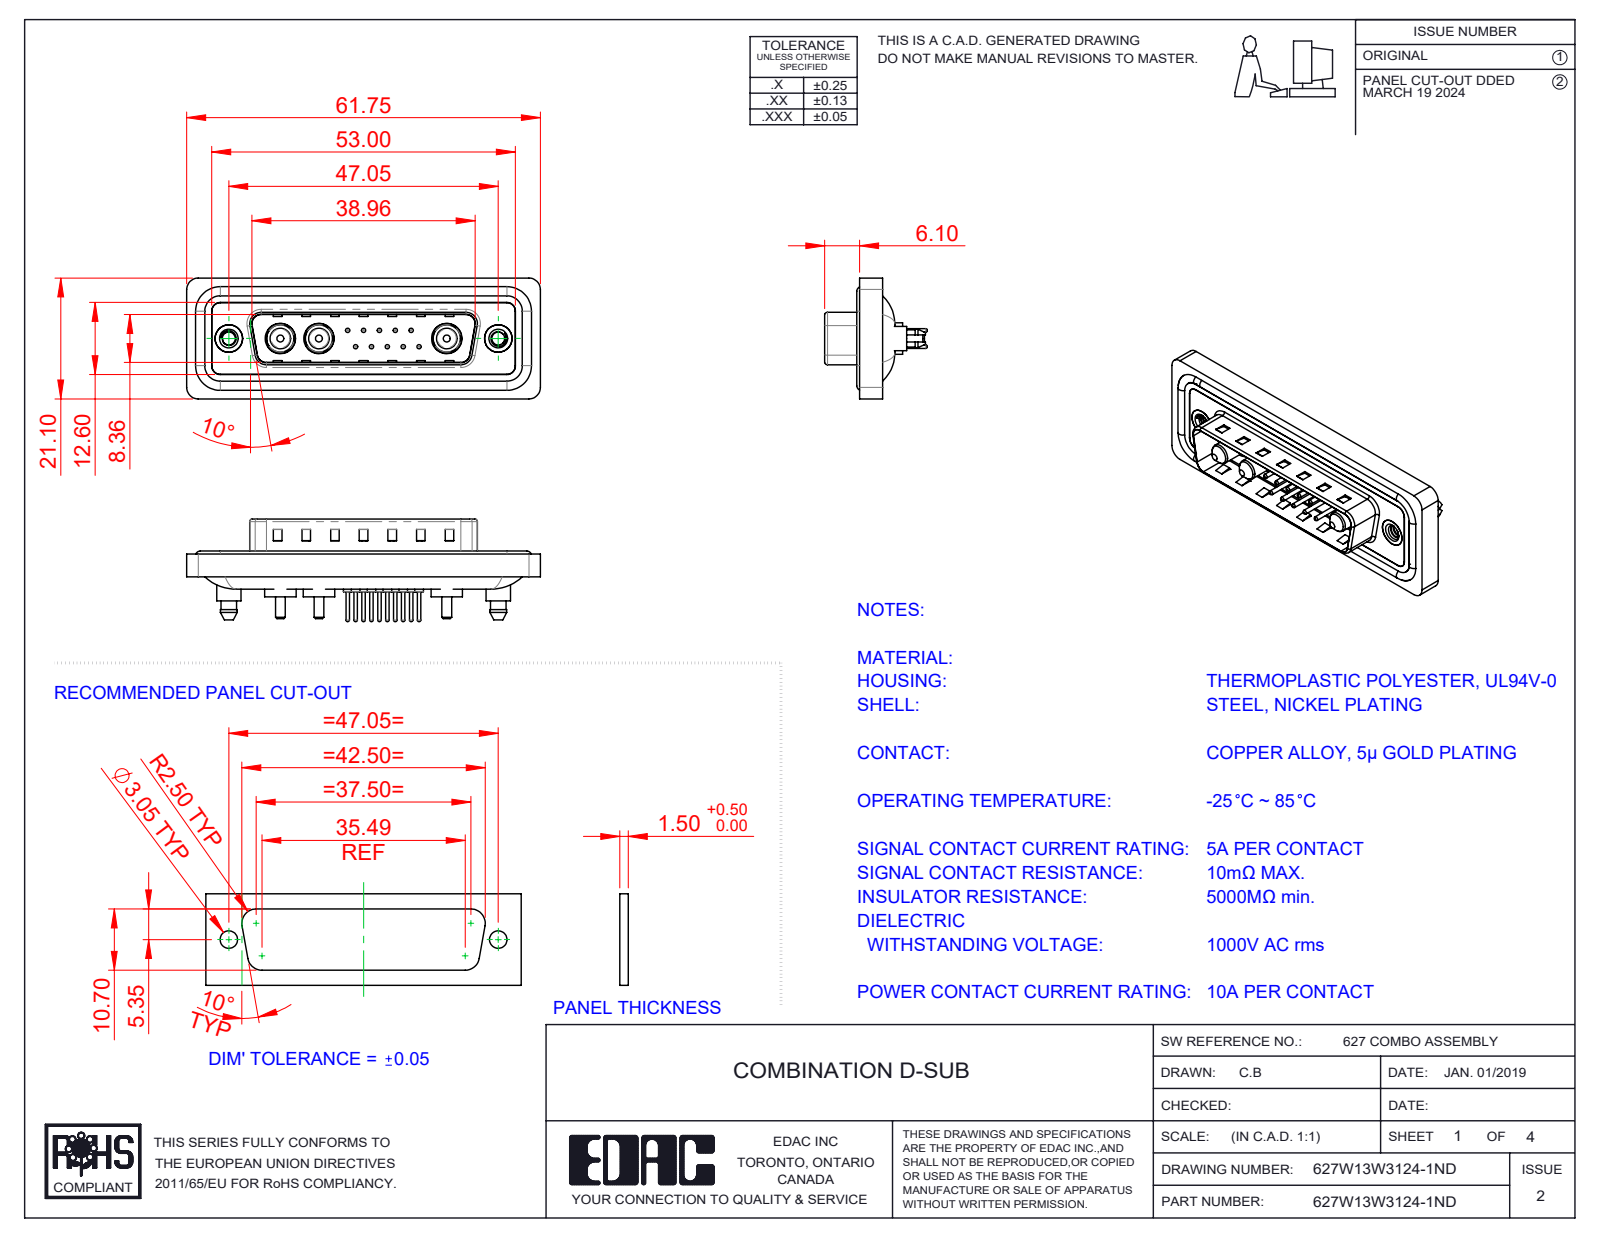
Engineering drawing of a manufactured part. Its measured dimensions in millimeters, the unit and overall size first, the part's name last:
Units: millimetres
Overall size (bounding box): 61.75 × 21.1 × 17.9
Round holes (diameter × count): ⌀0.75 ×10, ⌀1.6 ×10, ⌀2 ×10, ⌀4.85 ×3, ⌀5.3 ×3, ⌀2.26 ×2, ⌀4 ×2, ⌀4.8 ×2, ⌀5 ×2
Round bosses / shafts (diameter × count): ⌀1.5 ×10, ⌀0.6 ×10, ⌀1.6 ×4, ⌀5.5 ×3, ⌀5.2 ×3, ⌀4.75 ×3, ⌀3.75 ×3, ⌀3.6 ×3
Partial cylindrical surfaces — rounded edges, fillets, slot ends (radius × count): R1.5 ×24, R2 ×18, R1.6 ×10, R0.5 ×8, R0.25 ×4, R0.6 ×4, R0.65 ×4, R0.9 ×4
Main face-to-face distances: 0.4, 1.5, 1.1, 1.6, 0.5, 3.1, 2.9, 0.82, 9.58, 4.1
Hole centre spacings: 3.16, 2.77, 5.04, 5.54, 7.49, 5.03, 8.31, 10.11
Volume: 7 426 mm³ · Surface area: 12 173 mm²
Bodies: 23 solids, 1028 faces (325 planar, 425 cylindrical, 278 other)
Part name (STEP PRODUCT): 627Combo Shell Rear_25 Contacts; 627Combo Housing_13W3; 627Combo Threaded Boardlock_D; 627W13W3124-1ND (+6 more)
STEP written by: SolidWorks 2023 (CONFIG_CONTROL_DESIGN)
